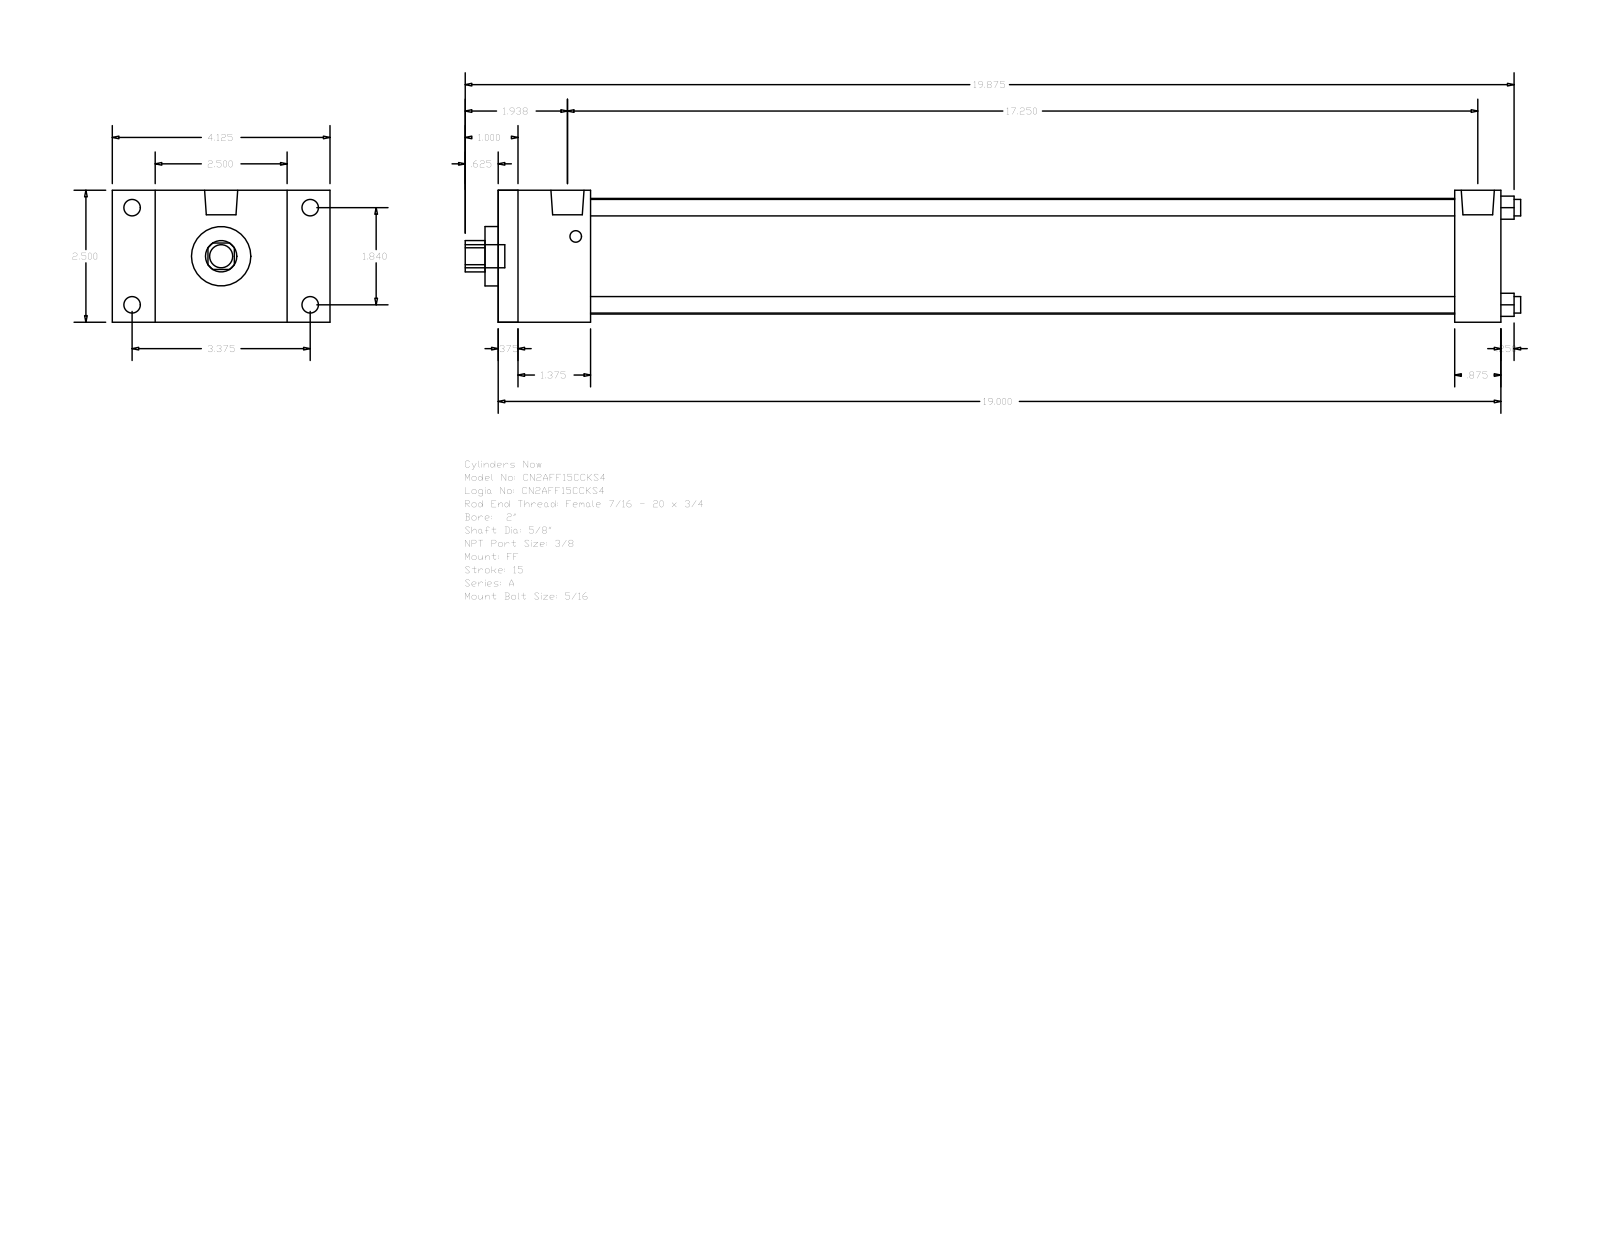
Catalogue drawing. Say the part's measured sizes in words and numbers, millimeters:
The part is named "A_FF__0200_0.625". Its 3-D file was written by "GSSL Pune (CONFIG_CONTROL_DESIGN)". It is 0 solids with 92 faces: 64 planar, 28 cylindrical and 0 other. Overall it measures 508 by 104.78 by 63.5 millimeters. Round holes: 4 of diameter 7.94, 1 of diameter 15.88, 1 of diameter 28.57, 1 of diameter 55.63. Round bosses or shafts: 4 of diameter 7.94, 4 of diameter 5.56, 2 of diameter 15.93, 1 of diameter 11.11. Partial cylindrical surfaces (rounded edges, fillets, slot ends): 1 of radius 7.54. The main face-to-face distances are 63.5, 482.6, 9.52, 473.08, 44.45, 460.37, 34.93, 450.85, 415.92, 438.15. The hole center spacings are 33.05, 46.74, 66.1.
